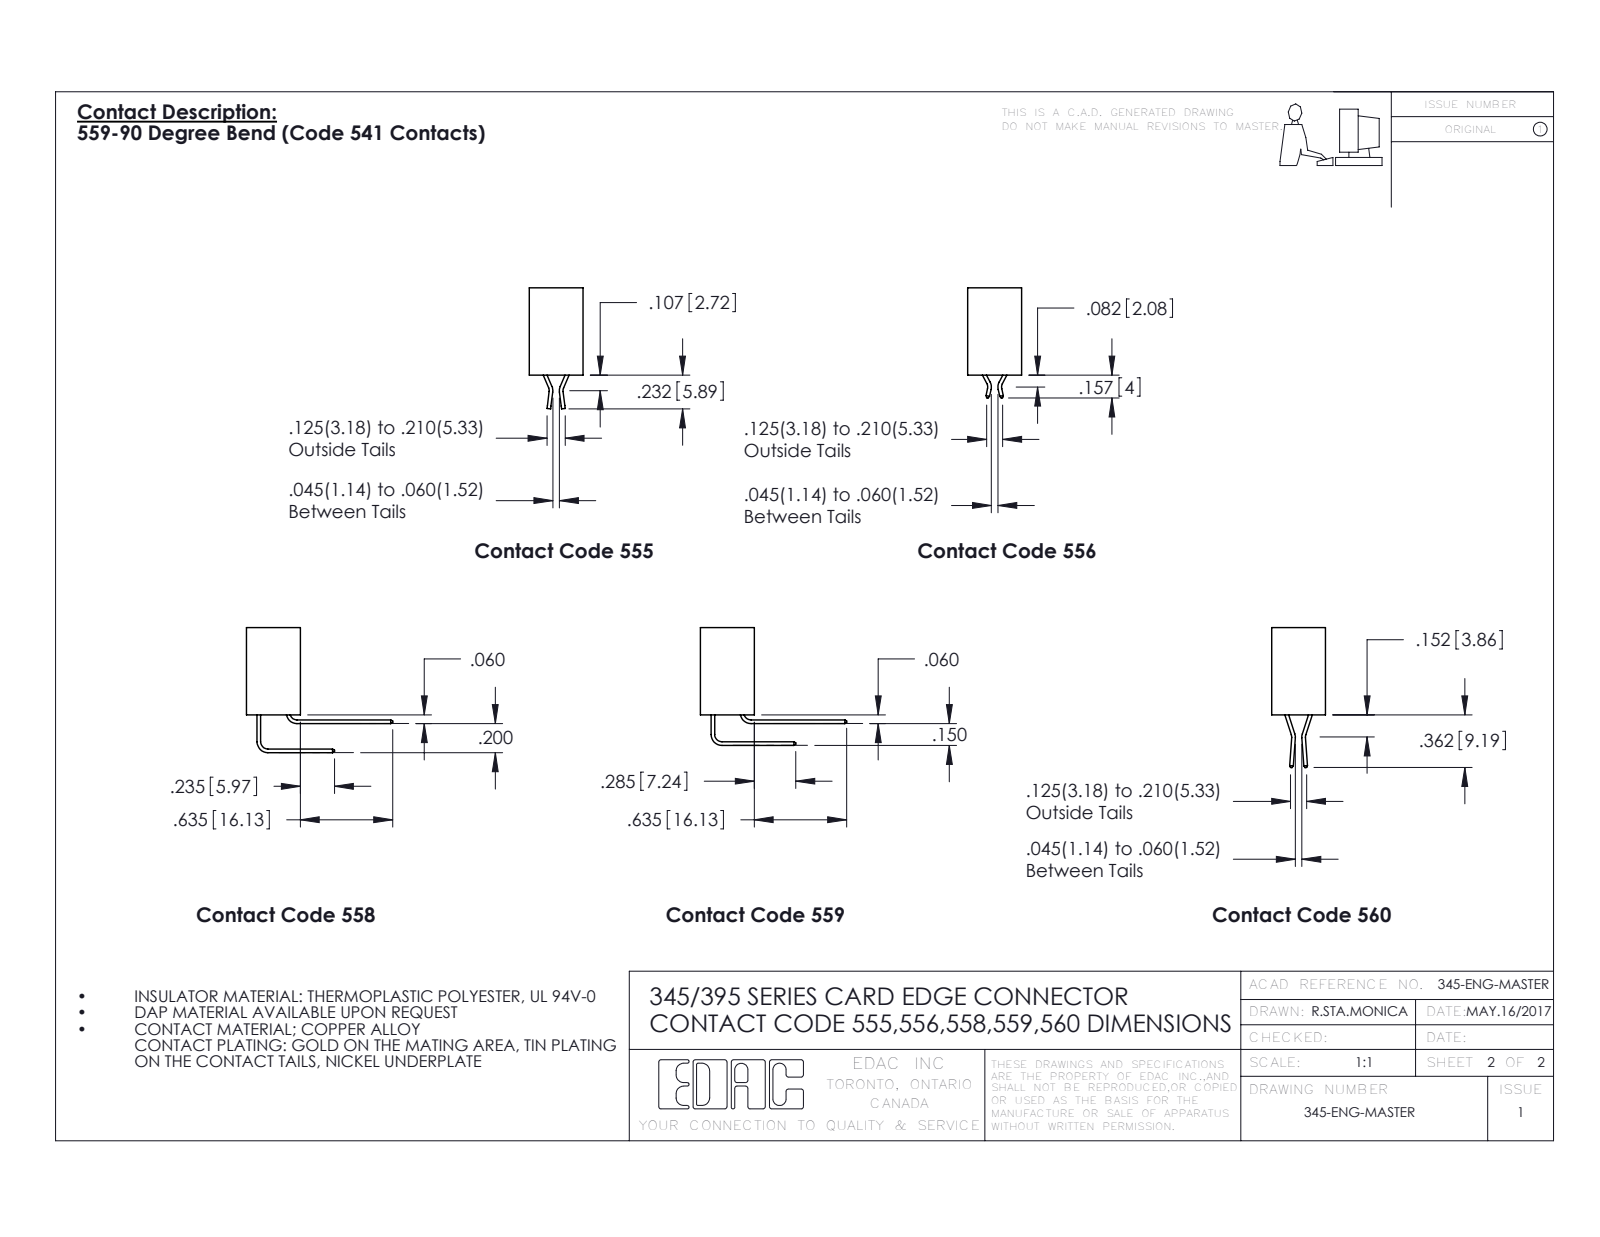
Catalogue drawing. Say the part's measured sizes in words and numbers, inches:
The part is named "345 Part_No Mounting Lugs; 345-292-001_345-293-124; 395-118-524-201". Its 3-D file was written by "SolidWorks 2016 (CONFIG_CONTROL_DESIGN)". It is 119 solids with 6490 faces: 4678 planar, 1812 cylindrical and 0 other. Overall it measures 6.16 by 0.762 by 0.37 inches. Its volume is 0.964 cubic inches and its surface area 36.44 square inches. Round holes: 1 of diameter 0.064. Partial cylindrical surfaces (rounded edges, fillets, slot ends): 177 of radius 0.006, 22 of radius 0.01, 6 of radius 0.007, 6 of radius 0.031, 3 of radius 0.026, 2 of radius 0.014, 2 of radius 0.019, 2 of radius 0.022. The main face-to-face distances are 0.298, 0.072, 0.2, 0.37, 0.098, 0.272, 0.025, 0.225, 0.072, 0.175.
